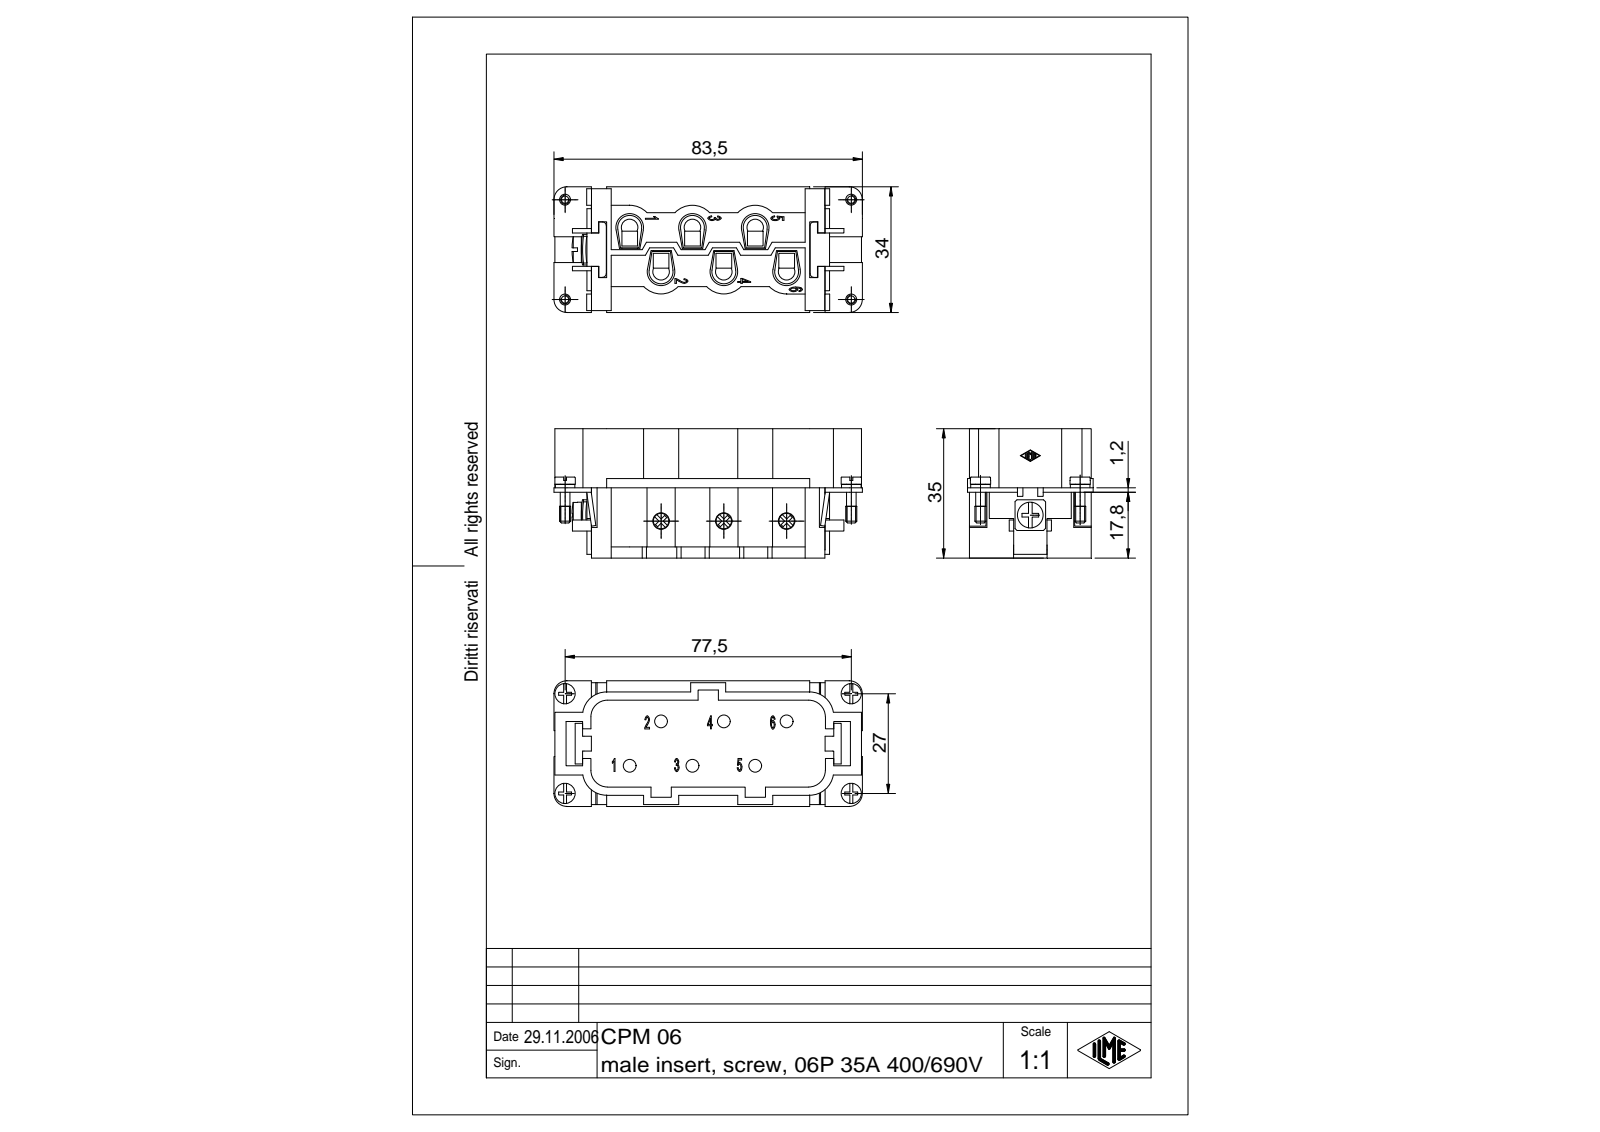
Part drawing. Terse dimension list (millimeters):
name: CPM 06
written by: Autodesk Inventor 7 (AUTOMOTIVE_DESIGN)
unit: mm
bodies: 3 solids, 950 faces (538 planar, 140 cylindrical, 272 other)
size: 83.5 × 35 × 34
volume: 37 800 mm³; area: 26 824 mm²
holes: 12× ⌀4.5, 1× ⌀3.24
bosses: 6× ⌀4.2, 6× ⌀3.5, 2× ⌀5.5, 2× ⌀5.3, 2× ⌀3, 2× ⌀2.6, 1× ⌀7
rounds: 14× R0.1, 10× R6.5, 6× R3.25, 6× R3.75, 4× R4.5, 2× R1, 2× R2, 2× R3.5
face distances: 2.5, 16, 18.5, 6.5, 2.25, 8, 4, 25.75, 3, 5.5
hole spacings: 17, 8.5, 14.71, 34, 25.5, 28.18, 42.5, 44.16
